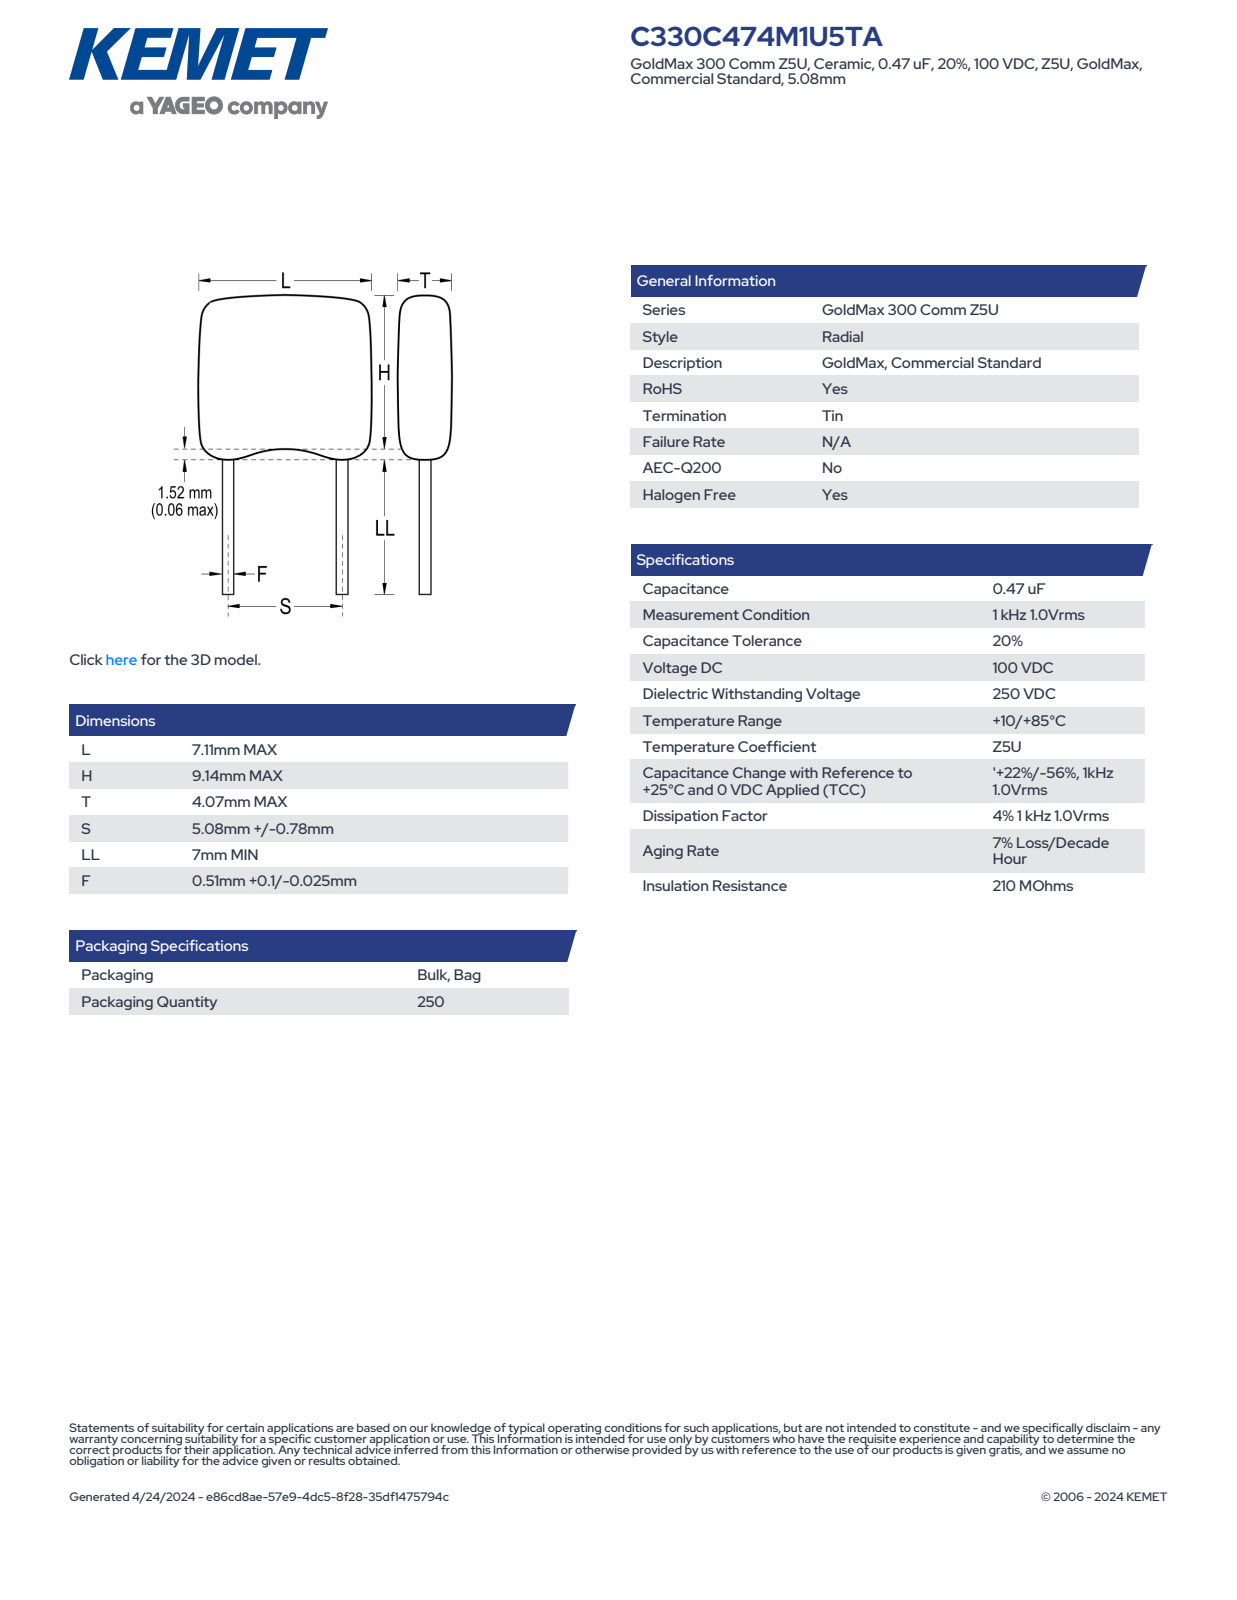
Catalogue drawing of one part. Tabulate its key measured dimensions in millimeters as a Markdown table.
| quantity | value |
| --- | --- |
| part name | CCR_KRCST_C330_L7.11H9.14T4.07S5.08LL7F0.61 |
| STEP written by | SolidWorks 2014 (AUTOMOTIVE_DESIGN) |
| units | millimeters |
| bodies | 4 solids, 83 faces (65 planar, 14 cylindrical, 4 other) |
| overall size | 17.66 × 7.11 × 4.08 |
| volume | 303 mm³ |
| surface area | 300 mm² |
| round bosses / shafts (diameter × count) | 0.61 × 2 |
| partial cylindrical surfaces (radius × count) | 0.75 × 10 |
| main face-to-face distances | 4.07, 7.11, 10.66, 4.08, 7, 17.66, 12.75, 5.75, 4.91, 11.99 |
